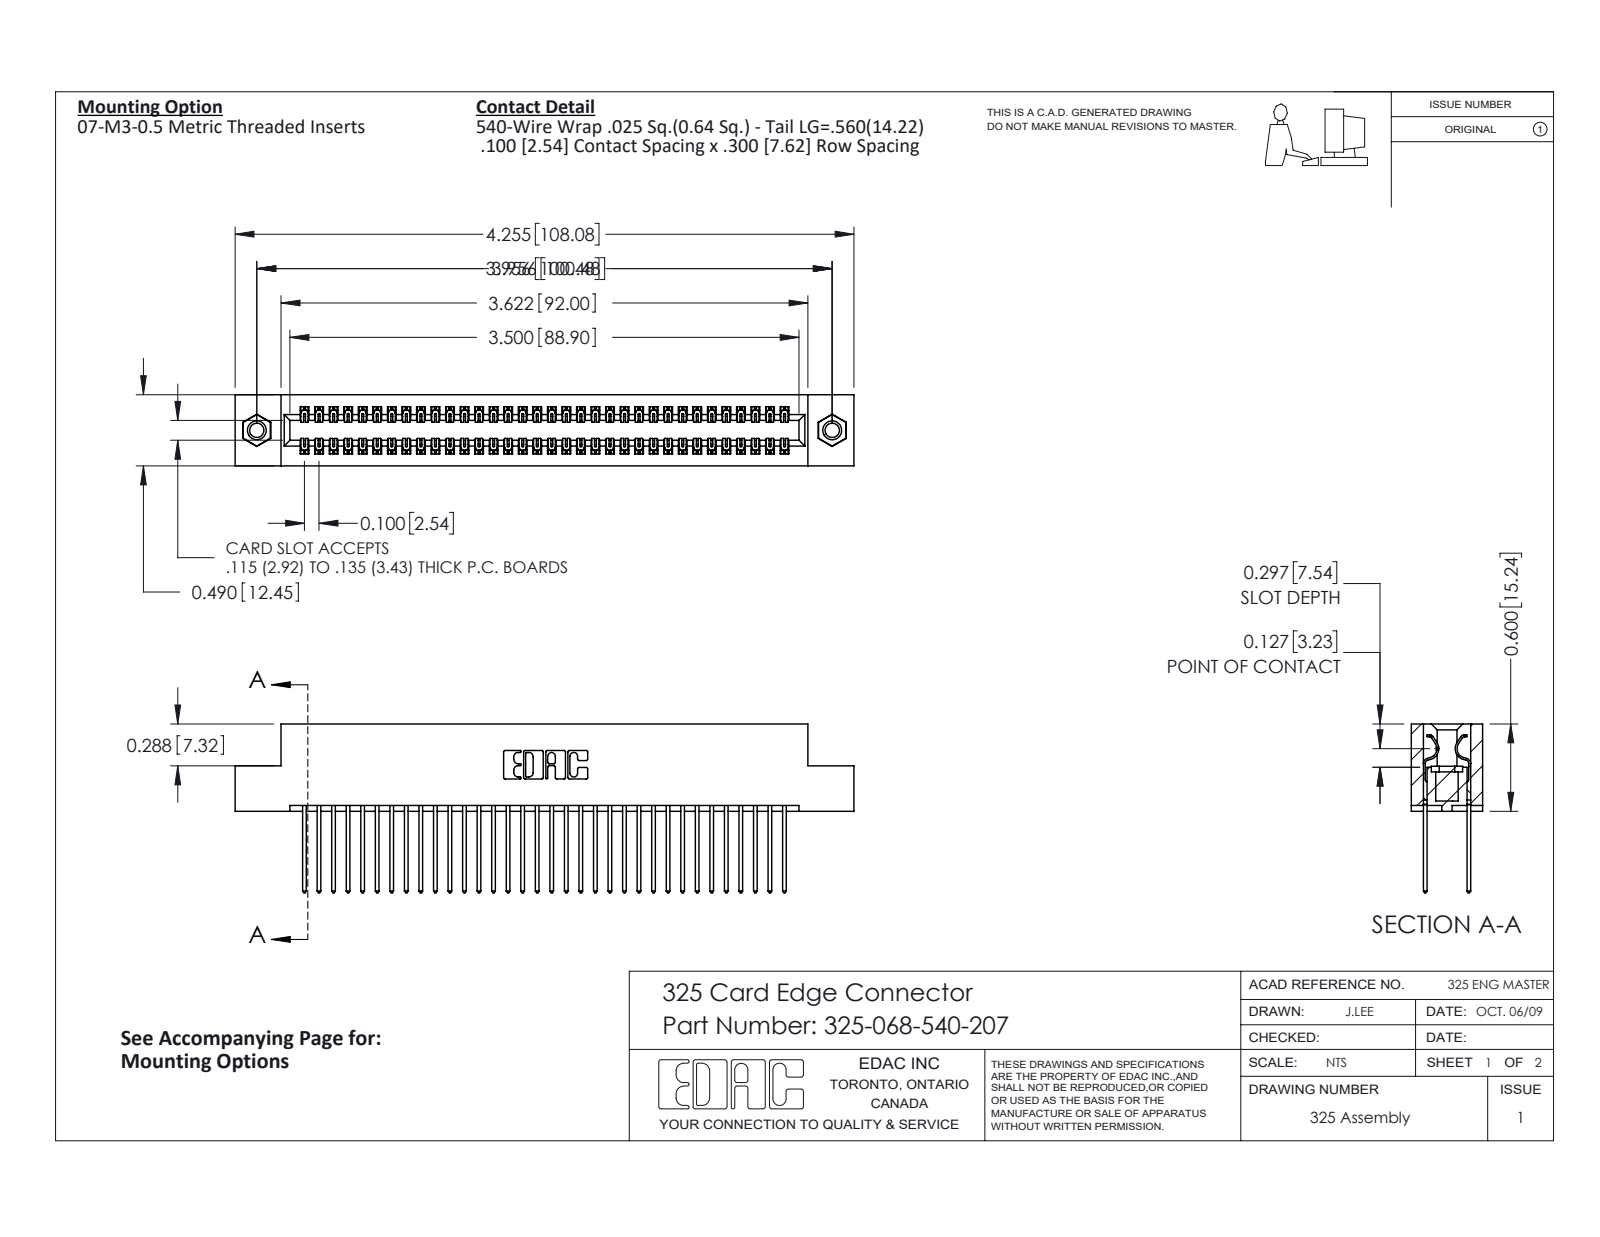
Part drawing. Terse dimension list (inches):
name: 325-068-540-207; 325-292-001_325-293-140; 325 Part_TI; 345-250-001_345-250-005-103
written by: SolidWorks 2016 (CONFIG_CONTROL_DESIGN)
unit: in
bodies: 71 solids, 3710 faces (2550 planar, 1144 cylindrical, 16 other)
size: 4.255 × 1.16 × 0.49
volume: 0.862 in³; area: 28.15 in²
holes: 2× ⌀0.098, 2× ⌀0.125, 2× ⌀0.16
bosses: 2× ⌀0.155
rounds: 102× R0.006, 68× R0.01, 22× R0.01, 6× R0.007, 6× R0.031, 3× R0.026, 2× R0.014, 2× R0.022
face distances: 0.083, 0.407, 0.3, 0.107, 0.383, 0.025, 0.49, 0.325, 0.275, 0.04
hole spacings: 3.956
